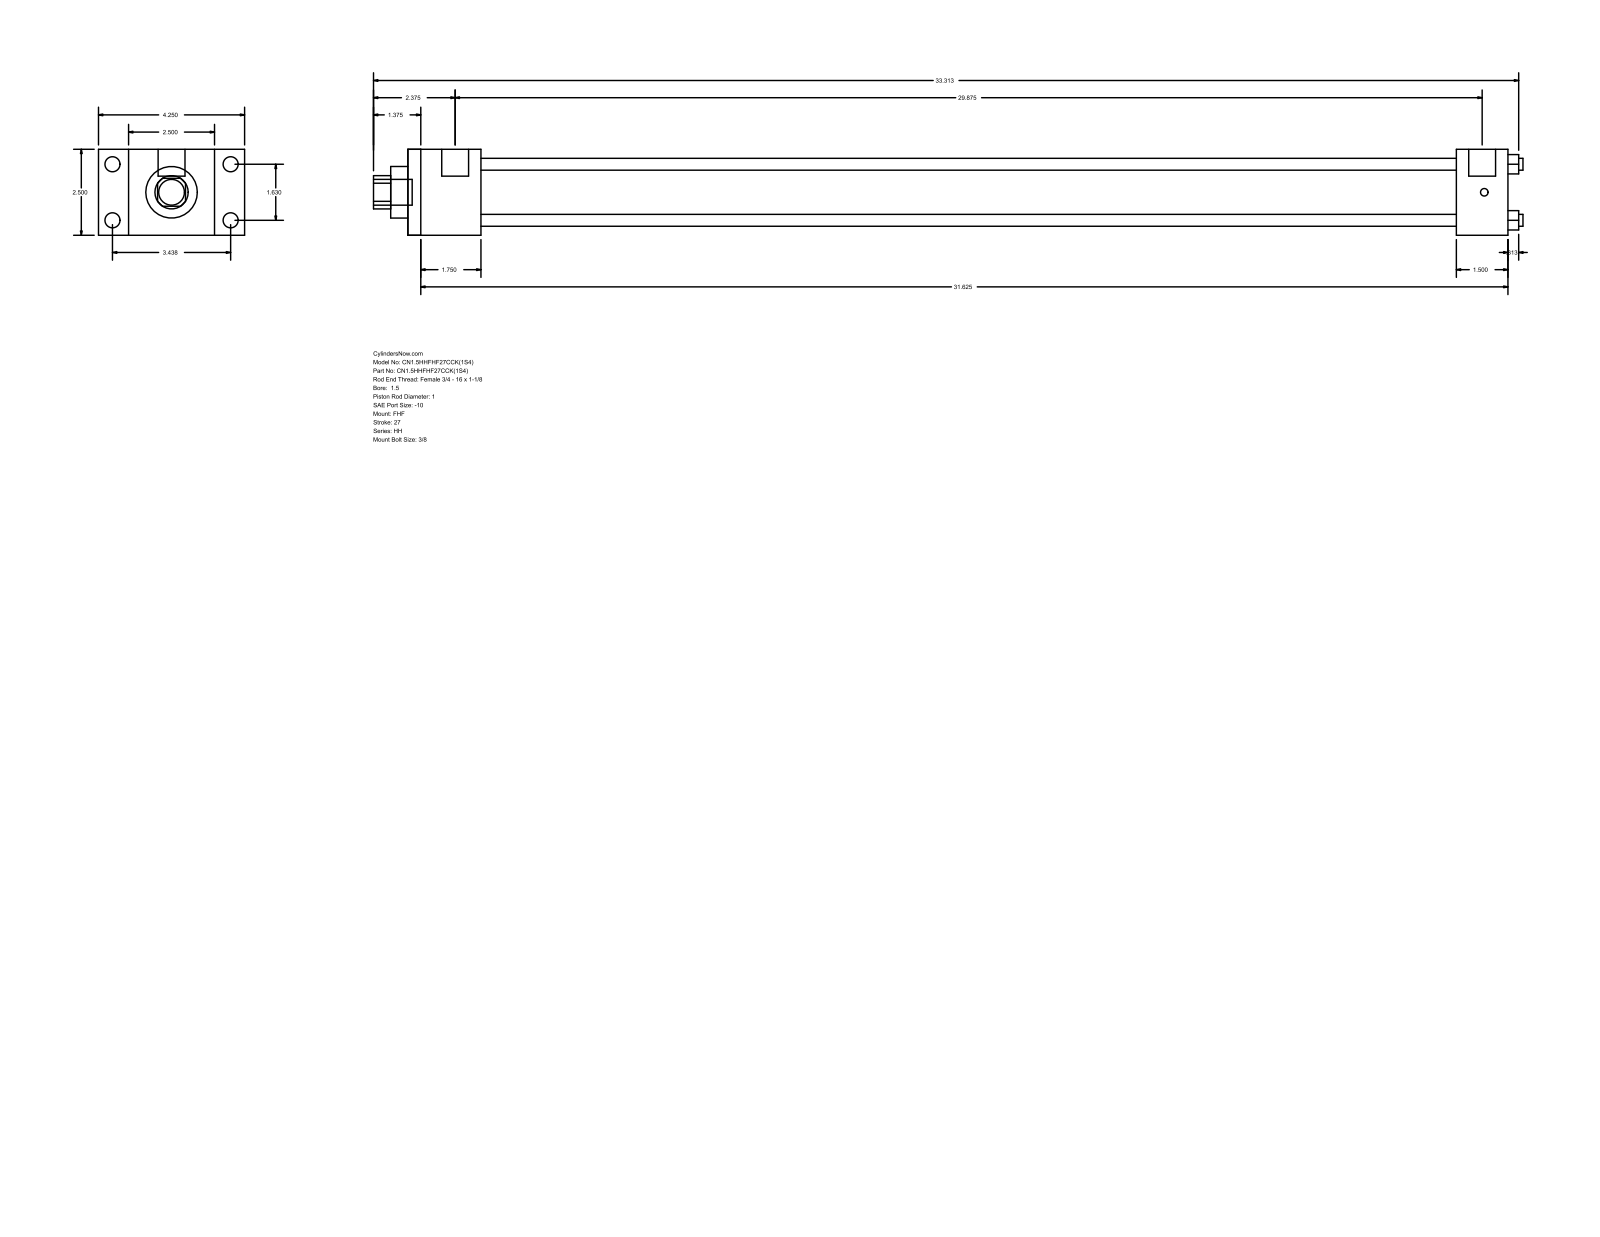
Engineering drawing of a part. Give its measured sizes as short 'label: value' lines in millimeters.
name: HH_FHF__0150_1
written by: GSSL Pune (CONFIG_CONTROL_DESIGN)
unit: mm
bodies: 0 solids, 88 faces (60 planar, 28 cylindrical, 0 other)
size: 849.31 × 107.95 × 63.5
holes: 4× ⌀8.76, 1× ⌀25.4, 1× ⌀38.1, 1× ⌀44.45
bosses: 4× ⌀11.13, 4× ⌀5.56, 2× ⌀19.84, 1× ⌀19.05
rounds: 1× R12.29
face distances: 63.5, 22.23, 85.73, 53.98, 107.96, 812.8, 758.82, 774.7, 720.72, 38.1
hole spacings: 29.27, 41.4, 58.55
